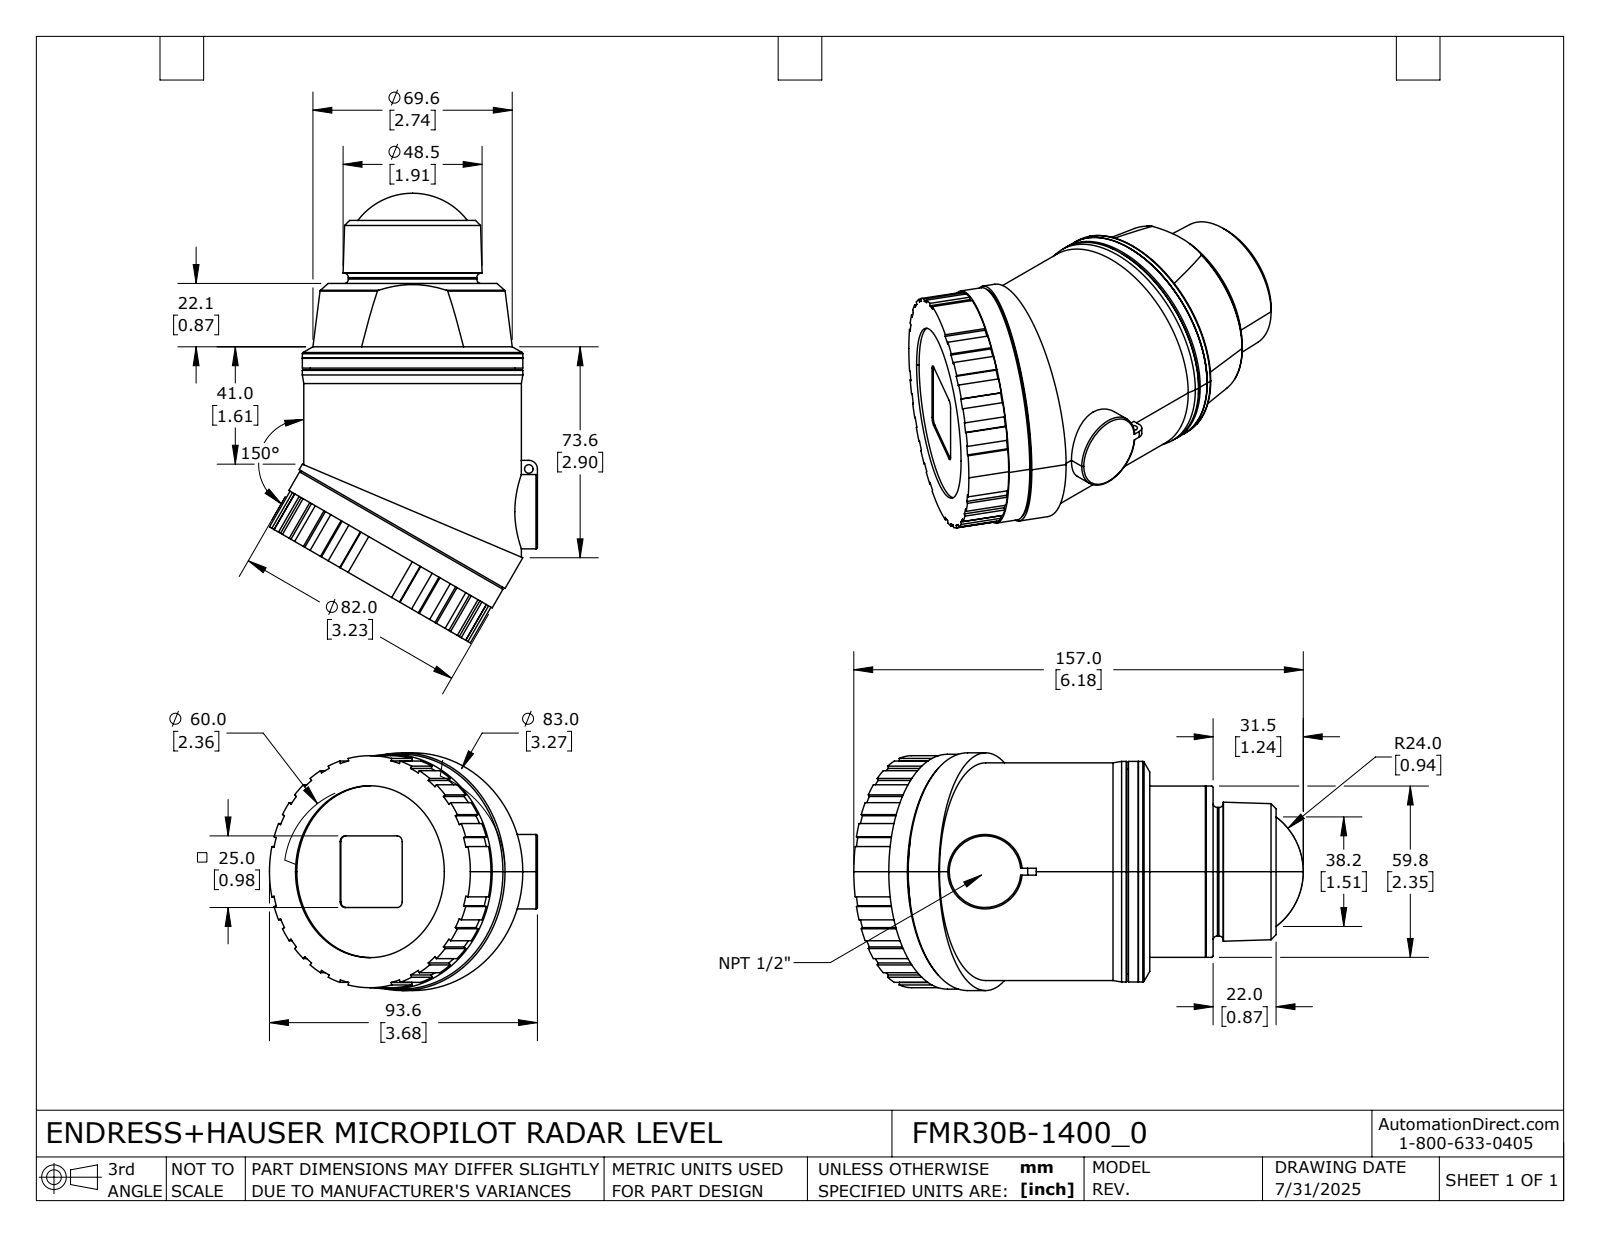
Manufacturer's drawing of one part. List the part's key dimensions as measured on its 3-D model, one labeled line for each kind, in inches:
Part name (STEP PRODUCT): FMR30B-1400_0
STEP written by: SolidWorks 2024 (AUTOMOTIVE_DESIGN)
Units: inches
Bodies: 1 solid, 240 faces (119 planar, 106 cylindrical, 15 other)
Overall size (bounding box): 7.712 × 4.528 × 4.528
Volume: 48.01 in³ · Surface area: 126.6 in²
Round holes (diameter × count): ⌀0.118 ×1, ⌀2.362 ×1
Round bosses / shafts (diameter × count): ⌀4.528 ×1, ⌀4.213 ×1, ⌀3.268 ×1, ⌀3.228 ×1, ⌀3.189 ×1, ⌀3.031 ×1, ⌀2.992 ×1, ⌀2.815 ×1
Partial cylindrical surfaces — rounded edges, fillets, slot ends (radius × count): R0.079 ×4, R0.177 ×4, R0.118 ×1, R1.559 ×1
Main face-to-face distances: 0.272, 0.142, 0.13, 0.406, 0.264, 0.134, 0.035, 0.346, 0.205, 0.075
